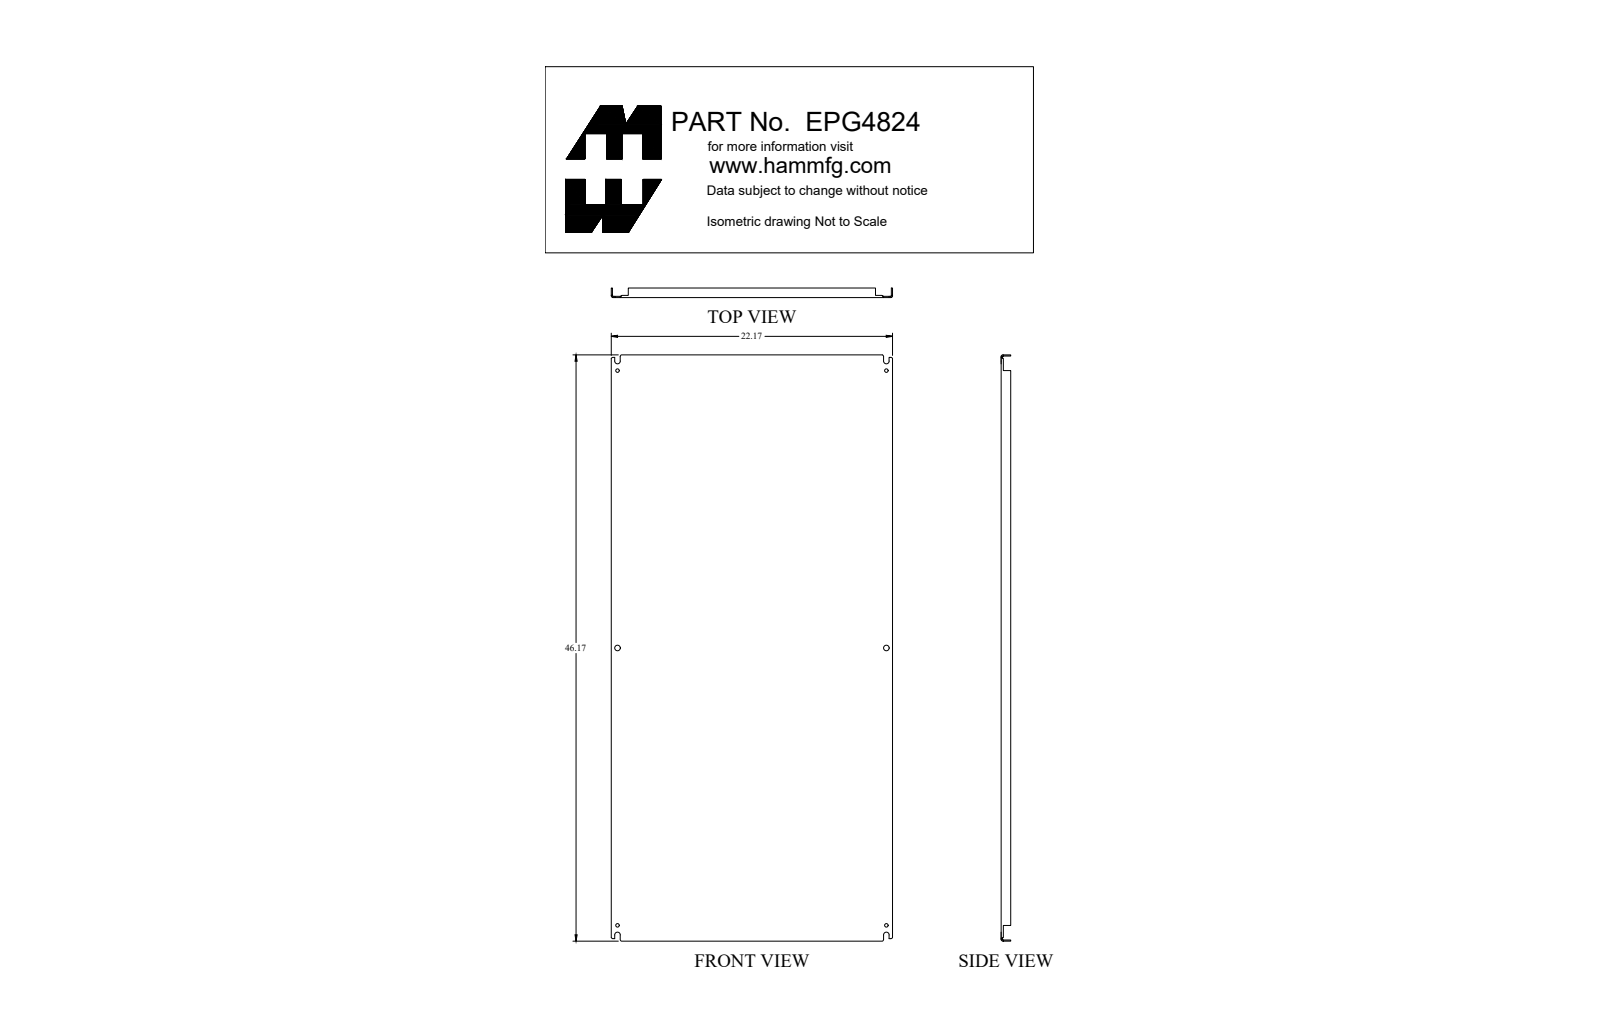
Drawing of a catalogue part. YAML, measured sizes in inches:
part_name: "EPG4824"
step_written_by: "SolidWorks 2018 (AUTOMOTIVE_DESIGN)"
units: inches
bodies: {solids: 1, faces: 132, planar: 74, cylindrical: 42, other: 16}
overall_size: [46.17, 22.17, 0.75]
volume: 104.4
surface_area: 2213
round_holes:
  - {diameter: 0.281, count: 4}
  - {diameter: 0.437, count: 2}
partial_cylinders:
  - {radius: 0.048, count: 4}
  - {radius: 0.063, count: 4}
  - {radius: 0.143, count: 4}
  - {radius: 0.219, count: 4}
face_to_face_distances: [0.095, 22.075, 21.98, 22.17, 46.075, 0.75, 0.655, 45.98, 46.17, 0.171]
hole_center_spacings: [21.844, 30.432, 21.188, 43.688, 48.555]
